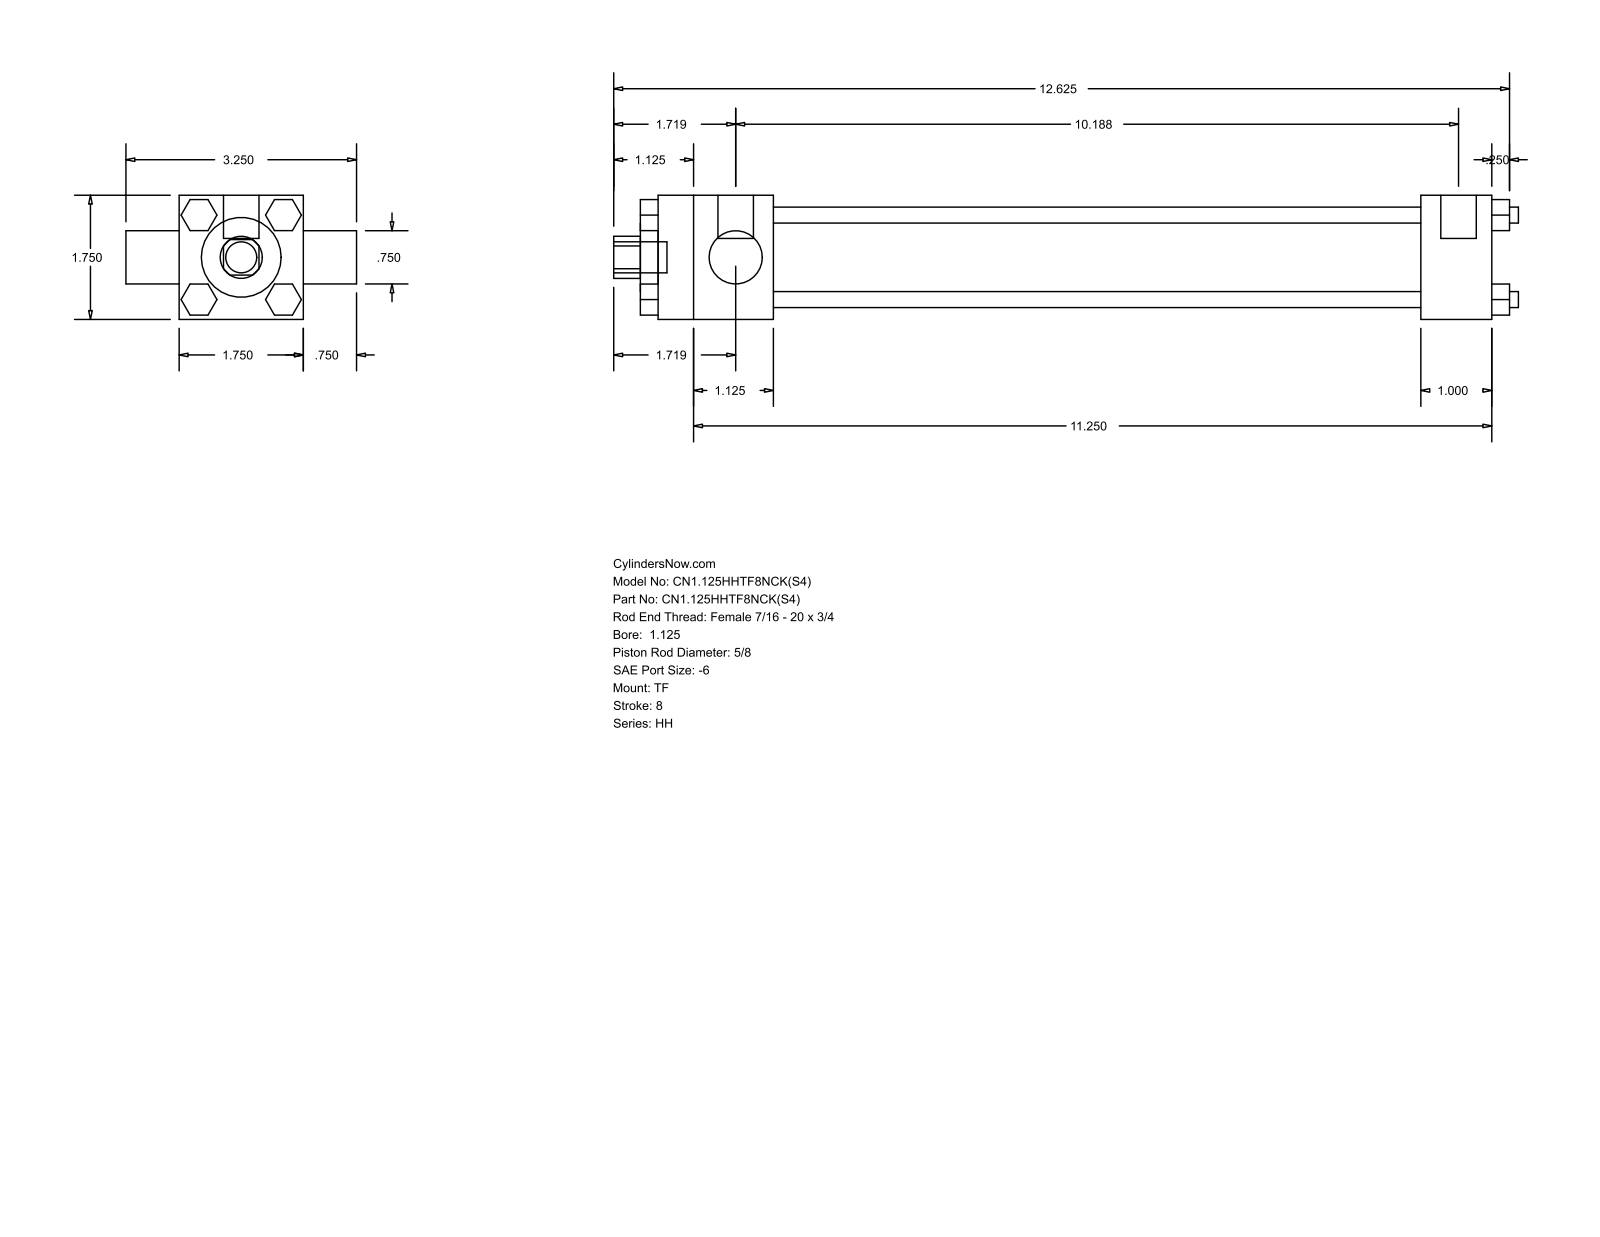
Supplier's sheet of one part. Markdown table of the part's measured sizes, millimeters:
| quantity | value |
| --- | --- |
| part name | HH_TF__0112_0.625 |
| STEP written by | GSSL Pune (CONFIG_CONTROL_DESIGN) |
| units | millimeters |
| bodies | 0 solids, 120 faces (92 planar, 28 cylindrical, 0 other) |
| overall size | 323.85 × 82.55 × 44.45 |
| round holes (diameter × count) | 15.88 × 1, 19.05 × 1, 28.57 × 1, 34.92 × 1 |
| round bosses / shafts (diameter × count) | 5.71 × 4, 5.56 × 3, 12.7 × 2, 11.11 × 1 |
| partial cylindrical surfaces (radius × count) | 7.54 × 1 |
| main face-to-face distances | 44.46, 11.11, 231.78, 257.17, 25.39, 41.27, 273.05, 298.44, 47.62, 6.35 |
